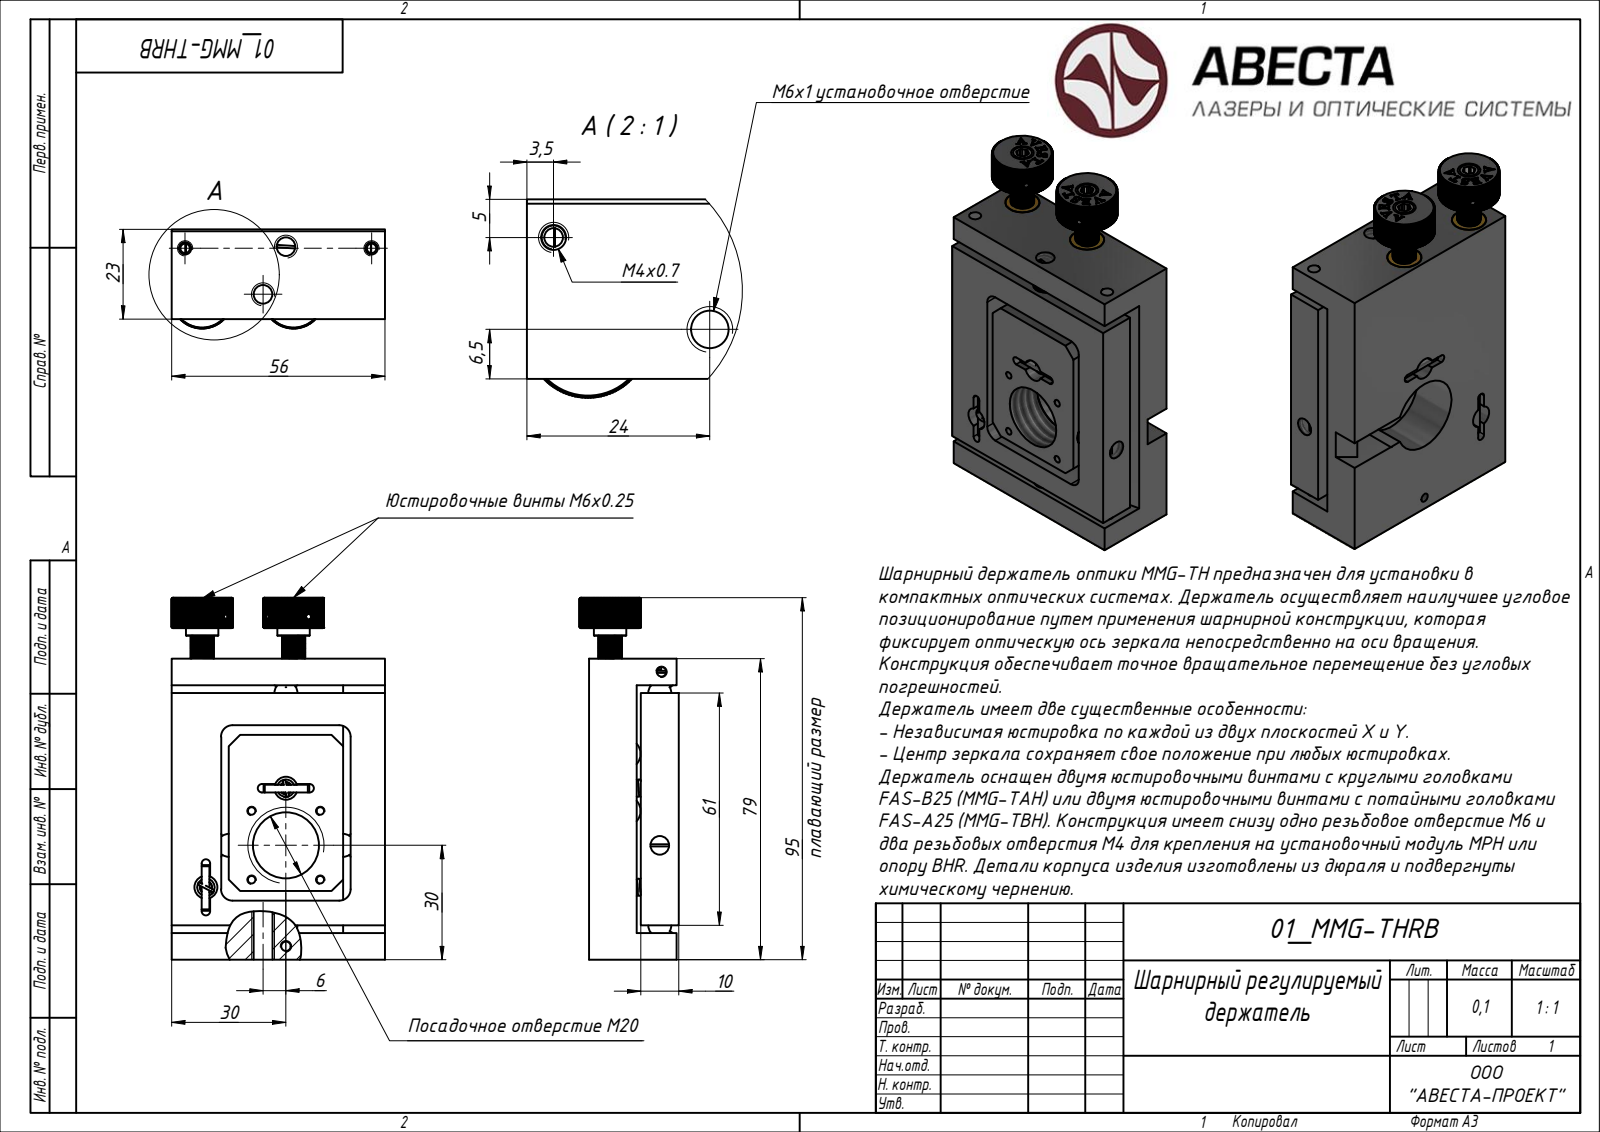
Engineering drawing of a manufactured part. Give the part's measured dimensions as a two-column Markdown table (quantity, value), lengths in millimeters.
| quantity | value |
| --- | --- |
| STEP written by | ST-DEVELOPER v15 (AUTOMOTIVE_DESIGN) |
| units | millimeters |
| bodies | 25 solids, 780 faces (340 planar, 0 cylindrical, 440 other) |
| overall size | 91.99 × 56 × 26.06 |
| volume | 85 334 mm³ |
| surface area | 38 211 mm² |
| main face-to-face distances | 23.55, 13.55, 10, 12.5, 11.05, 1.05, 2, 9, 56, 7 |
